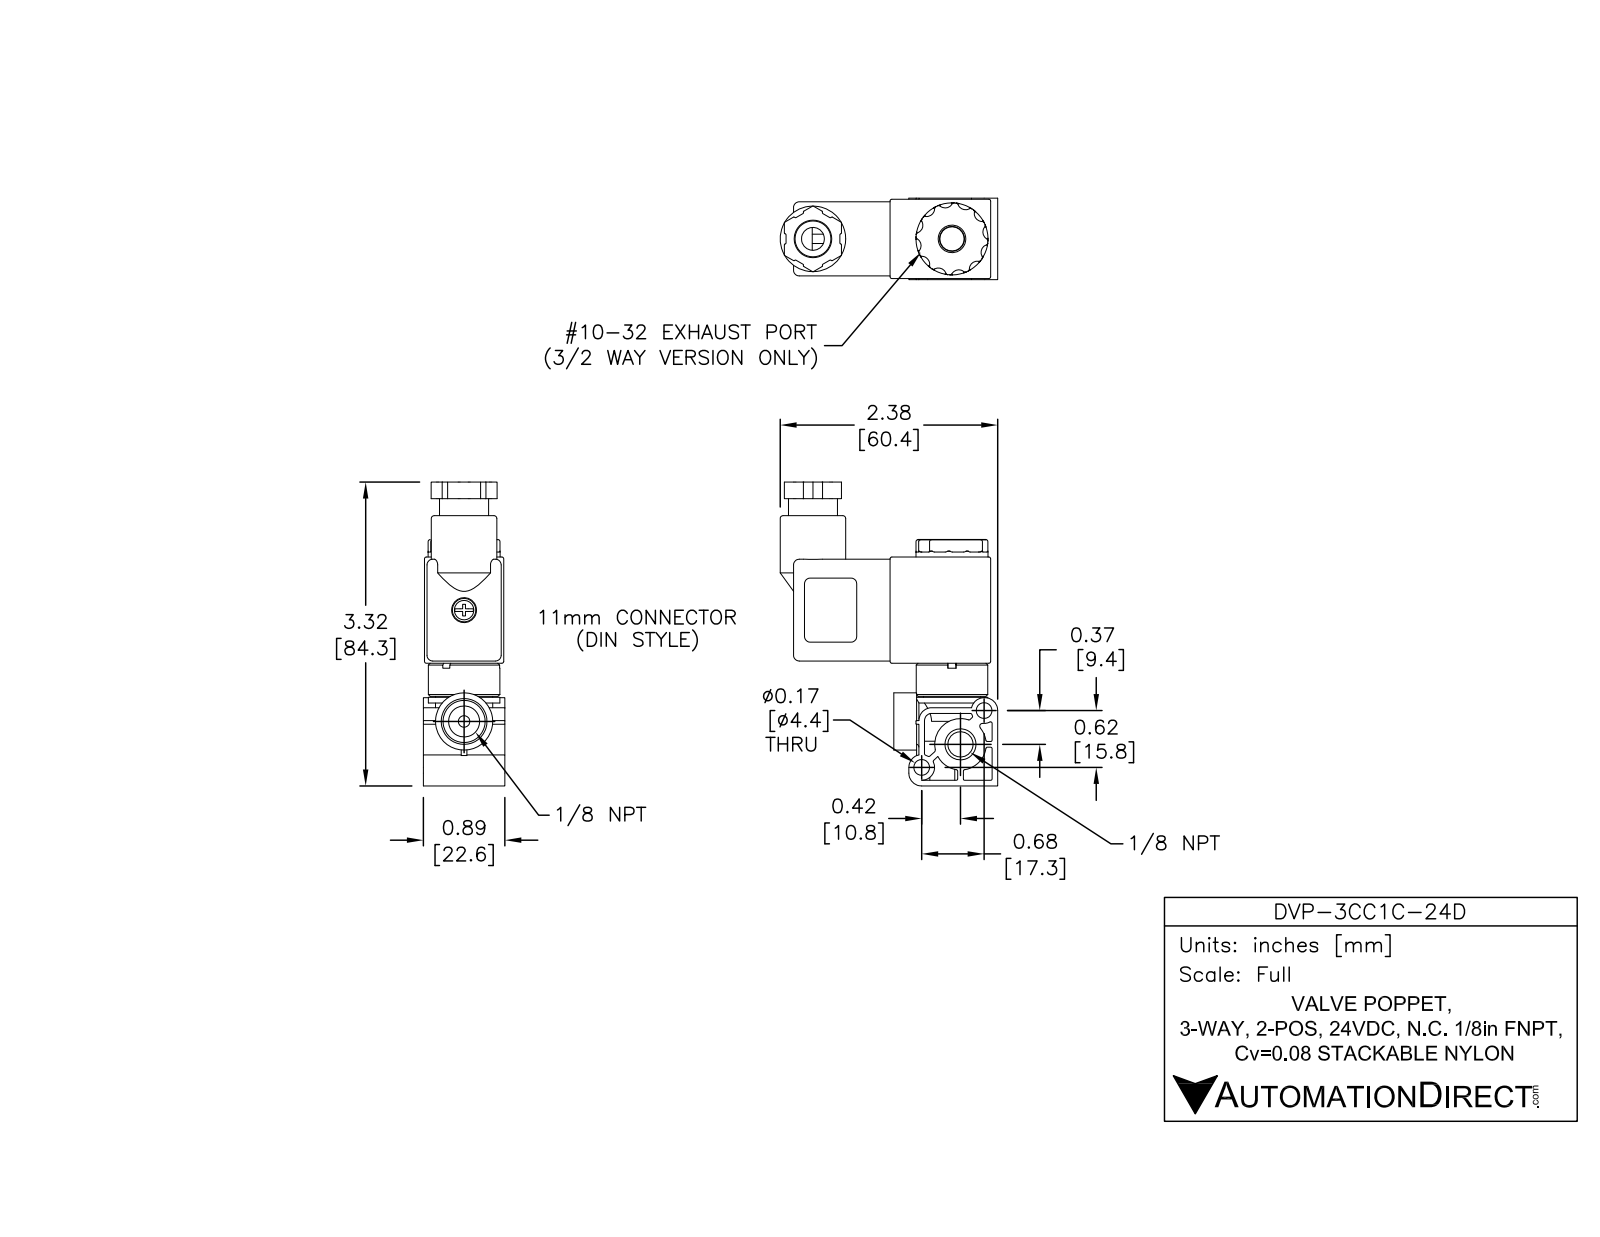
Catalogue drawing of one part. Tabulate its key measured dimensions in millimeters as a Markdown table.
| quantity | value |
| --- | --- |
| part name | DVP-3CC1C-24D |
| STEP written by | SolidWorks 2015 (AUTOMOTIVE_DESIGN) |
| units | millimeters |
| bodies | 5 solids, 1465 faces (664 planar, 318 cylindrical, 483 other) |
| overall size | 84 × 60.4 × 22.6 |
| volume | 34 870 mm³ |
| surface area | 25 320 mm² |
| round holes (diameter × count) | 2.5 × 2, 3.2 × 2, 3.8 × 2, 4.4 × 2, 8.6 × 2, 1.4 × 1, 2.3 × 1, 2.6 × 1, 4.2 × 1, 5 × 1, 6.4 × 1, 6.8 × 1 |
| round bosses / shafts (diameter × count) | 15.9 × 2, 20 × 1, 19.8 × 1, 18.2 × 1, 16.6 × 1, 14.5 × 1, 13.6 × 1, 13.3 × 1 |
| partial cylindrical surfaces (radius × count) | 0.4 × 28, 0.3 × 25, 0.6 × 24, 0.5 × 12, 1.6 × 12, 2.2 × 12, 0.8 × 5, 3.6 × 4 |
| main face-to-face distances | 2, 20, 1.3, 20.3, 19.3, 0.7, 21.3, 22, 18, 22.3 |
| hole center spacings | 8.3, 10.7, 11.4, 12.5, 13.3, 18.6, 23.4, 24 |
